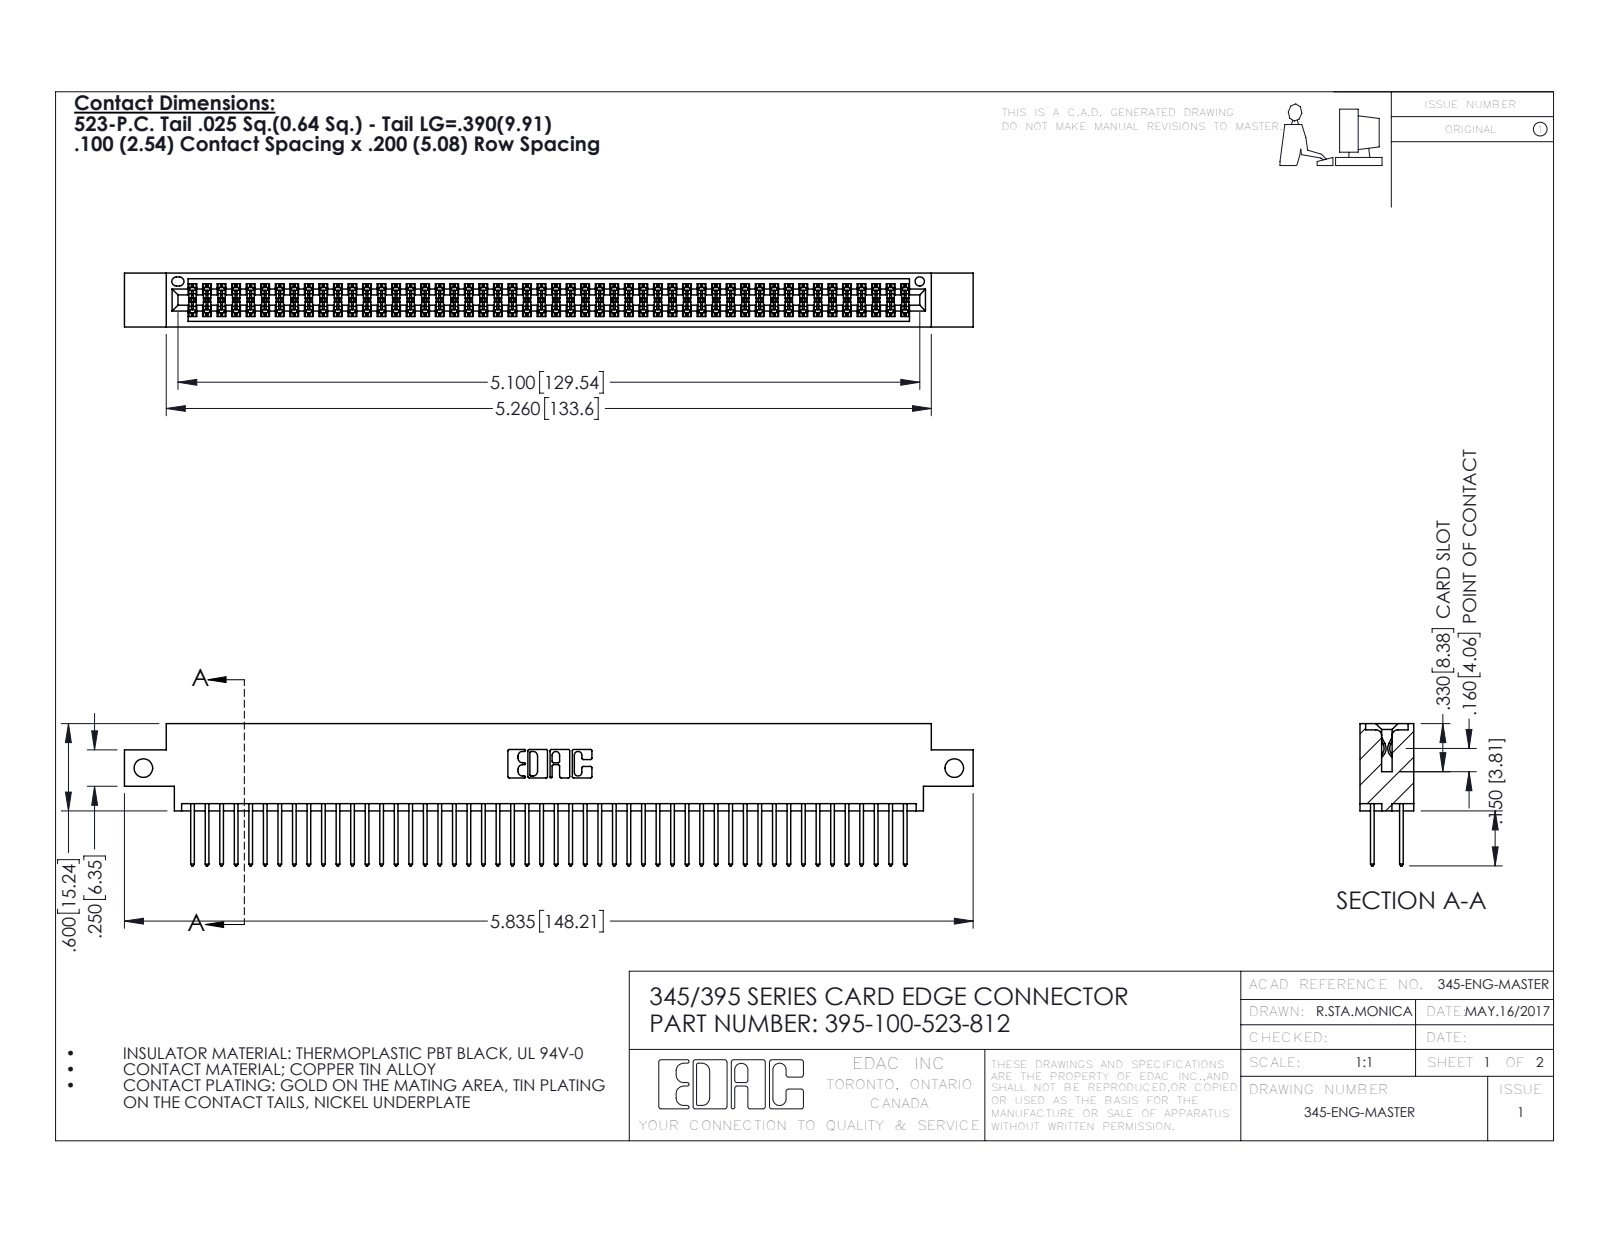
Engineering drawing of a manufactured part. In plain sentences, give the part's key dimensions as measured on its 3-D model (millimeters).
The part is named "345 Part_0.170 Offset - Side Mount; 345-292-001_345-293-123; 395-100-523-812". Its 3-D file was written by "SolidWorks 2016 (CONFIG_CONTROL_DESIGN)". It is 101 solids with 5130 faces: 3384 planar, 1746 cylindrical and 0 other. Overall it measures 148.2 by 24.8 by 9.4 millimeters. Its volume is 14 500 cubic millimeters and its surface area 22 480 square millimeters. Round holes: 2 of diameter 3.3, 1 of diameter 1.6. Partial cylindrical surfaces (rounded edges, fillets, slot ends): 150 of radius 0.2, 100 of radius 0.3, 22 of radius 0.3, 6 of radius 0.2, 6 of radius 0.8, 3 of radius 0.7, 2 of radius 0.4, 2 of radius 0.5. The main face-to-face distances are 1.8, 7.6, 5.1, 2.5, 6.9, 0.6, 9.4, 5.7, 4.4, 3.8. The hole center spacings are 141.6.
